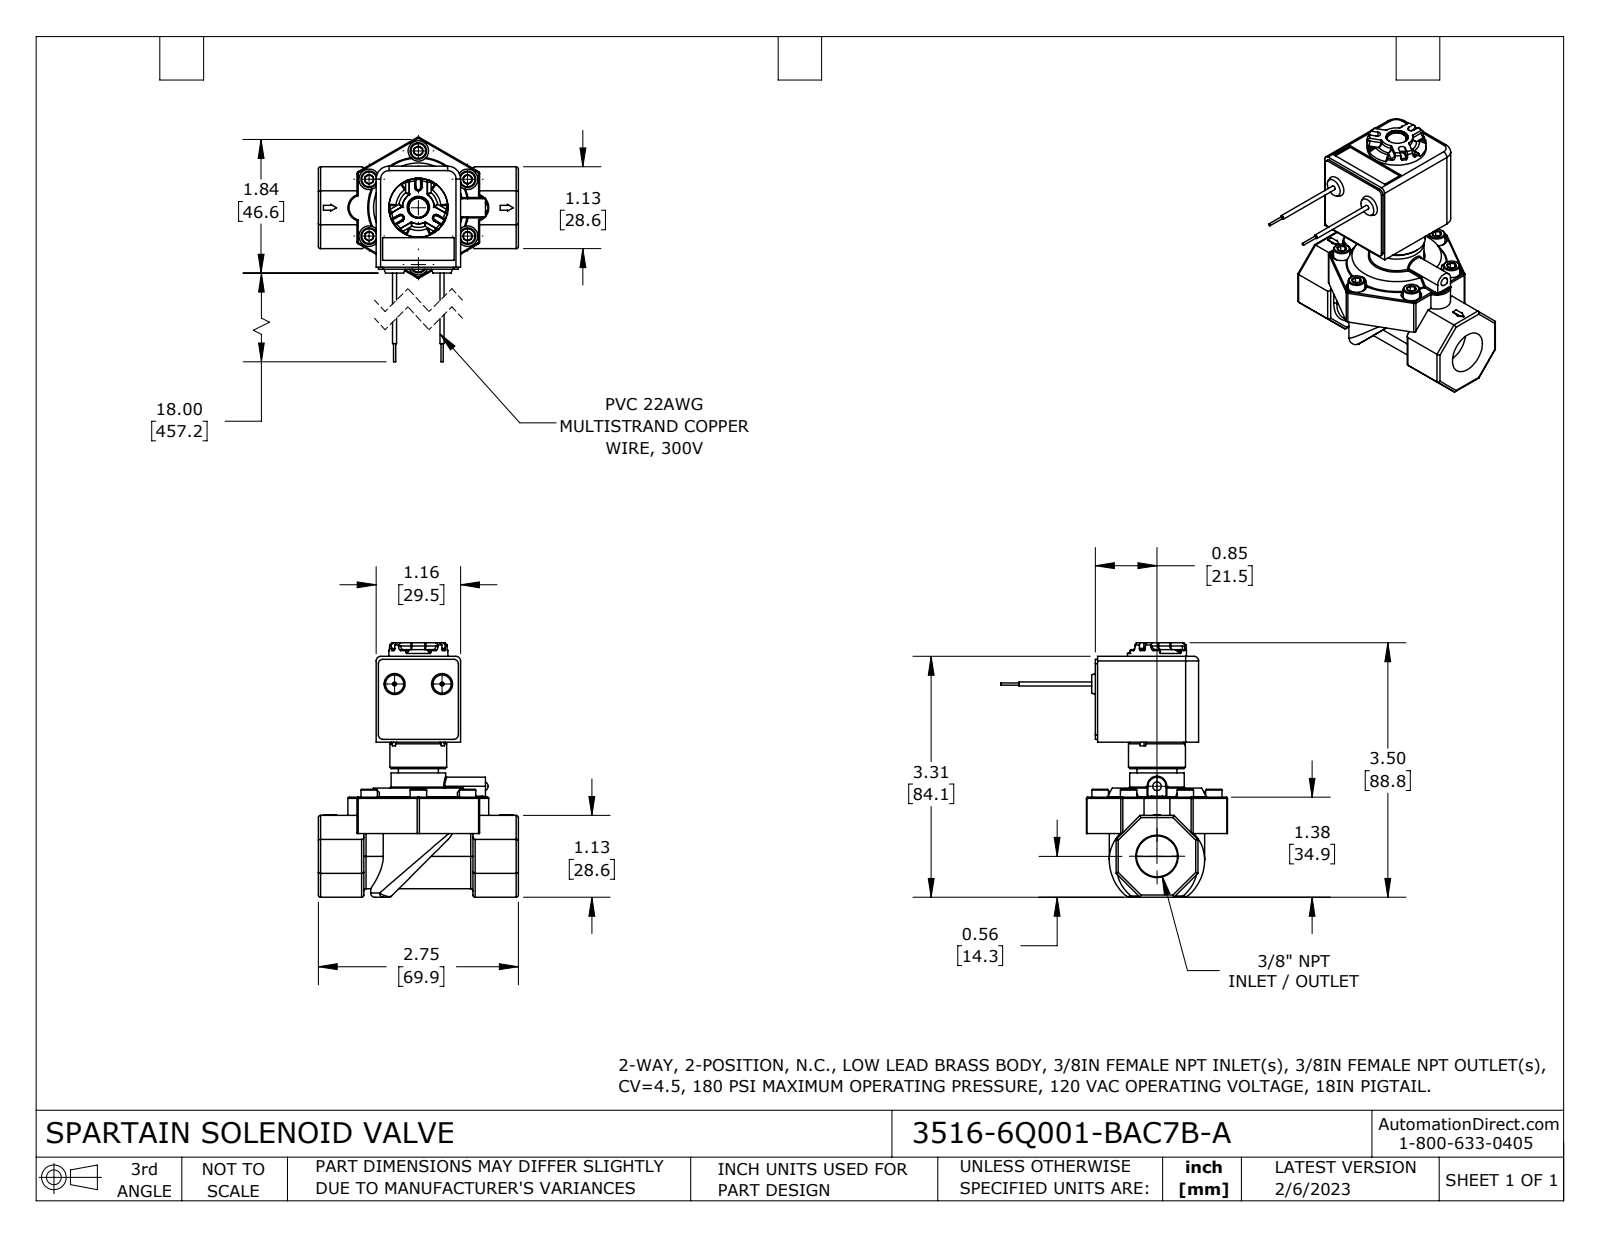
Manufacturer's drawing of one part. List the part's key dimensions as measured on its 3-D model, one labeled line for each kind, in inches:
Part name (STEP PRODUCT): 3516-6Q001-BAC7B-A
STEP written by: SolidWorks 2021 (CONFIG_CONTROL_DESIGN)
Units: inches
Bodies: 1 solid, 1187 faces (236 planar, 648 cylindrical, 303 other)
Overall size (bounding box): 3.497 × 3.117 × 2.75
Volume: 4.616 in³ · Surface area: 49.45 in²
Round holes (diameter × count): ⌀0.104 ×6, ⌀0.156 ×6, ⌀0.218 ×6, ⌀0.281 ×6, ⌀0.093 ×2, ⌀0.136 ×2, ⌀0.047 ×1, ⌀0.062 ×1, ⌀0.065 ×1, ⌀0.09 ×1, ⌀0.092 ×1, ⌀0.119 ×1
Round bosses / shafts (diameter × count): ⌀0.212 ×7, ⌀0.226 ×6, ⌀0.138 ×6, ⌀0.097 ×6, ⌀0.156 ×2, ⌀0.03 ×2, ⌀1.29 ×1, ⌀0.812 ×1
Partial cylindrical surfaces — rounded edges, fillets, slot ends (radius × count): R0.03 ×30, R0.015 ×19, R0.062 ×15, R0.125 ×9, R0.156 ×8, R0.031 ×6, R0.05 ×6, R0.044 ×3
Main face-to-face distances: 1.125, 1.161, 0.794, 1.955, 0.25, 1.687, 1.005, 0.625, 0.016, 1.021
Hole centre spacings: 0.781, 1.353, 0.404, 1.105, 1.509, 1.562, 0.71, 0.8
